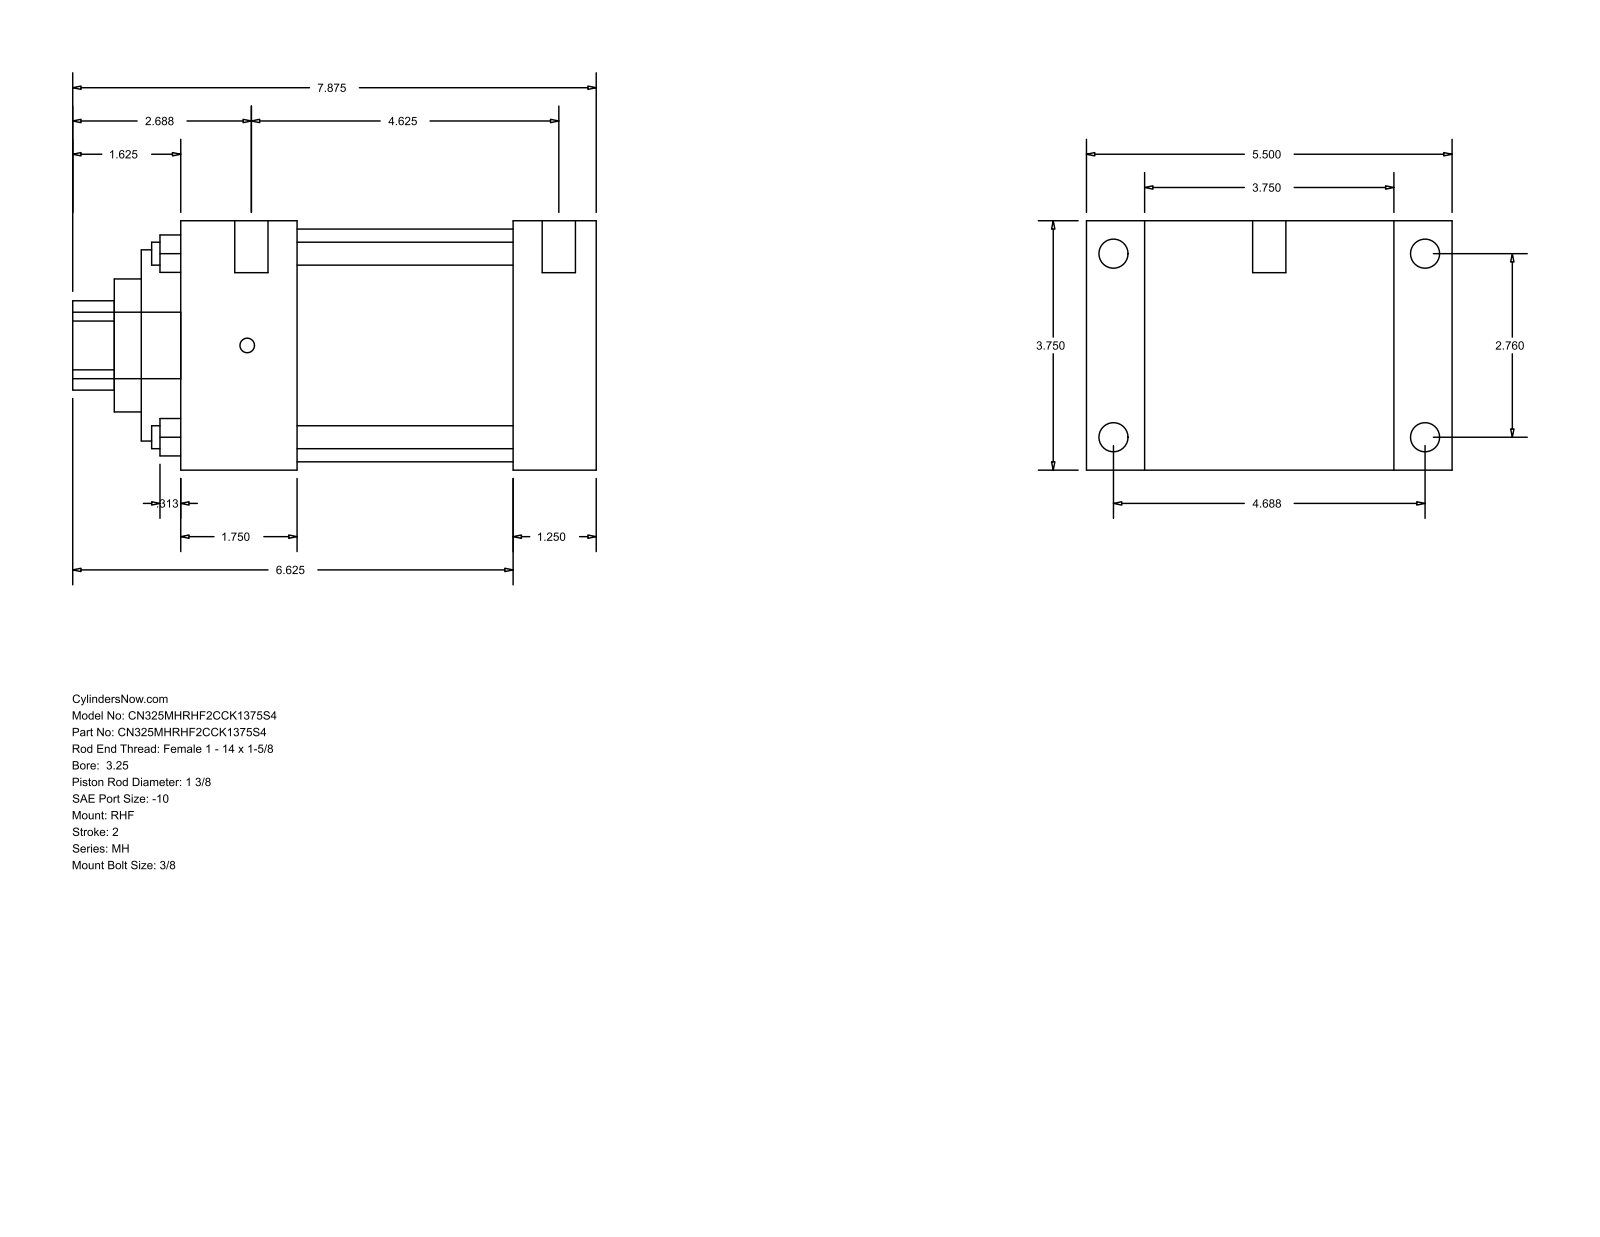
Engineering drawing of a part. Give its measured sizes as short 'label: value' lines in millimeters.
name: MH_RHF__0325_1.375
written by: GSSL Pune (CONFIG_CONTROL_DESIGN)
unit: mm
bodies: 0 solids, 90 faces (61 planar, 29 cylindrical, 0 other)
size: 200.03 × 139.7 × 95.25
holes: 4× ⌀8.76, 1× ⌀34.92, 1× ⌀50.8, 1× ⌀73.03, 1× ⌀88.9
bosses: 4× ⌀11.13, 4× ⌀5.56, 2× ⌀12.7, 1× ⌀25.4
rounds: 1× R17.06
face distances: 95.24, 31.75, 22.23, 117.47, 127.01, 158.76, 139.7, 44.45, 82.56, 114.31
hole spacings: 49.57, 70.1, 99.14
